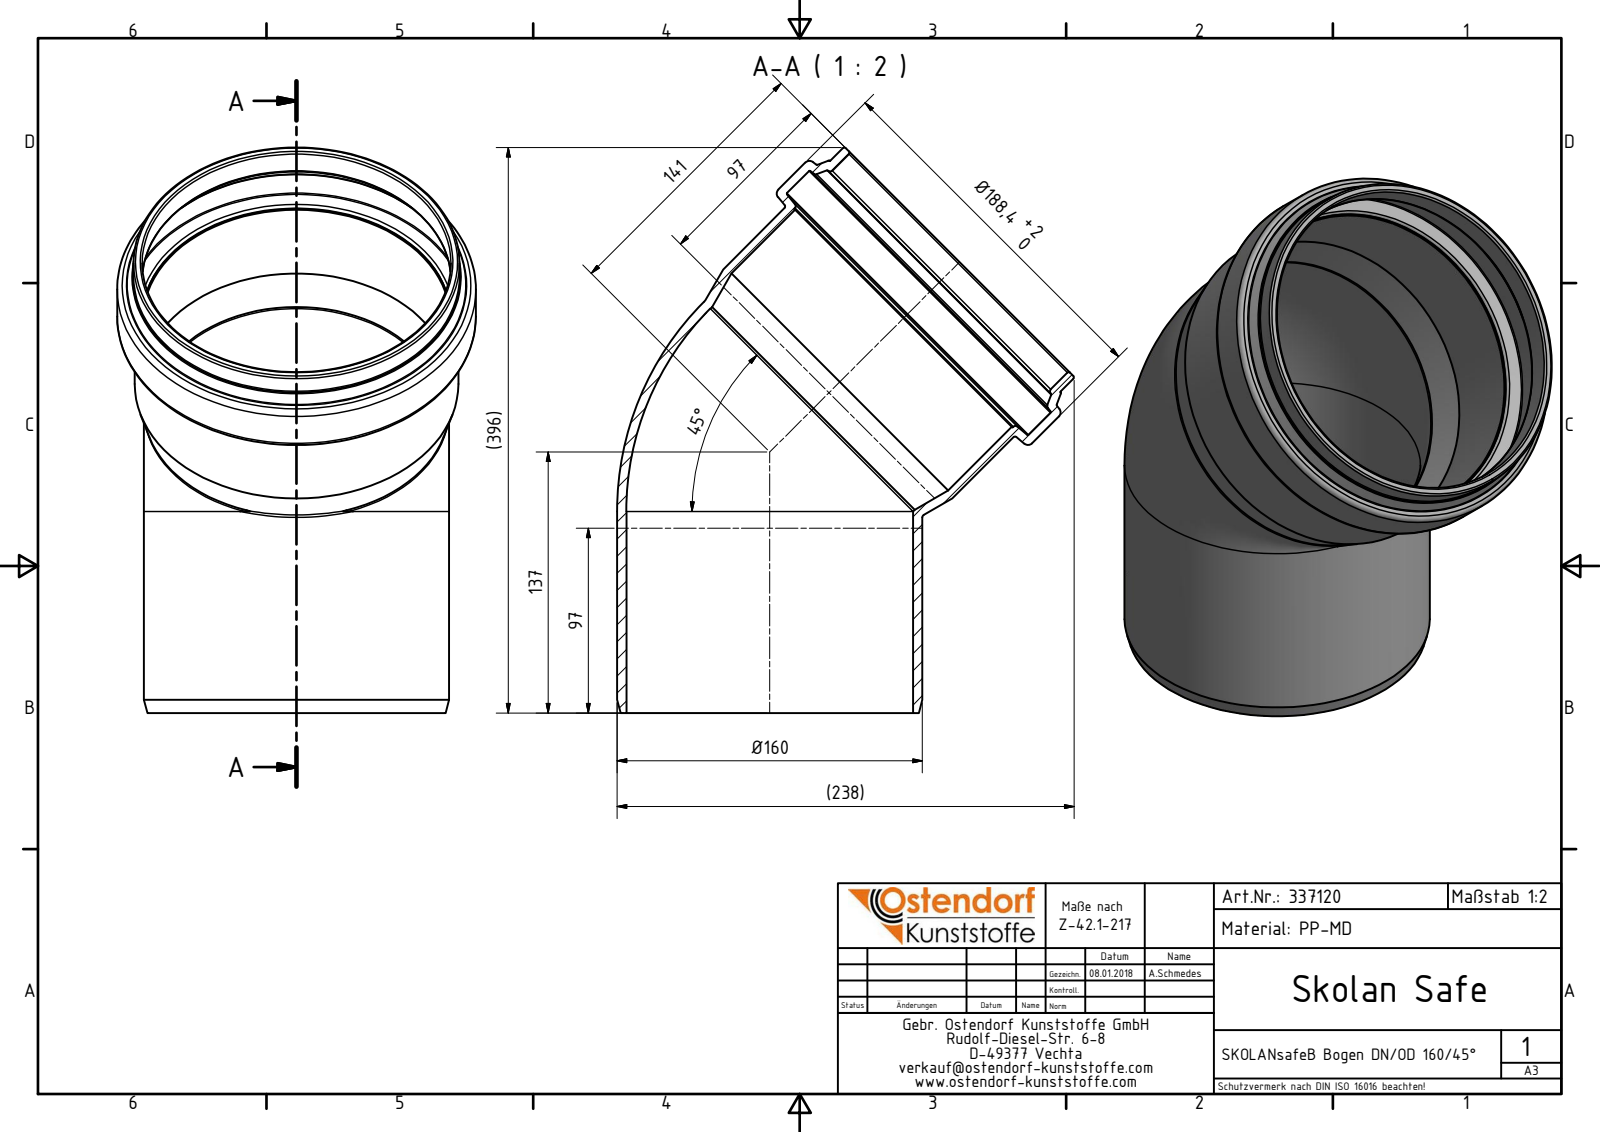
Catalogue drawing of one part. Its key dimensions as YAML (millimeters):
part_name: "337120 SKOLANsafeB Bogen DN_OD 160_45°"
step_written_by: "Autodesk Inventor 2016 (AUTOMOTIVE_DESIGN)"
units: millimeters
bodies: {solids: 1, faces: 42, planar: 3, cylindrical: 11, other: 28}
overall_size: [296.82, 239.97, 188.4]
volume: 649213
surface_area: 295357
round_holes:
  - {diameter: 150.5, count: 2}
  - {diameter: 162.2, count: 2}
  - {diameter: 161, count: 1}
  - {diameter: 179.4, count: 1}
round_bosses_or_shafts:
  - {diameter: 160.3, count: 2}
  - {diameter: 188.4, count: 1}
  - {diameter: 171.2, count: 1}
  - {diameter: 170, count: 1}
face_to_face_distances: [41.75]
